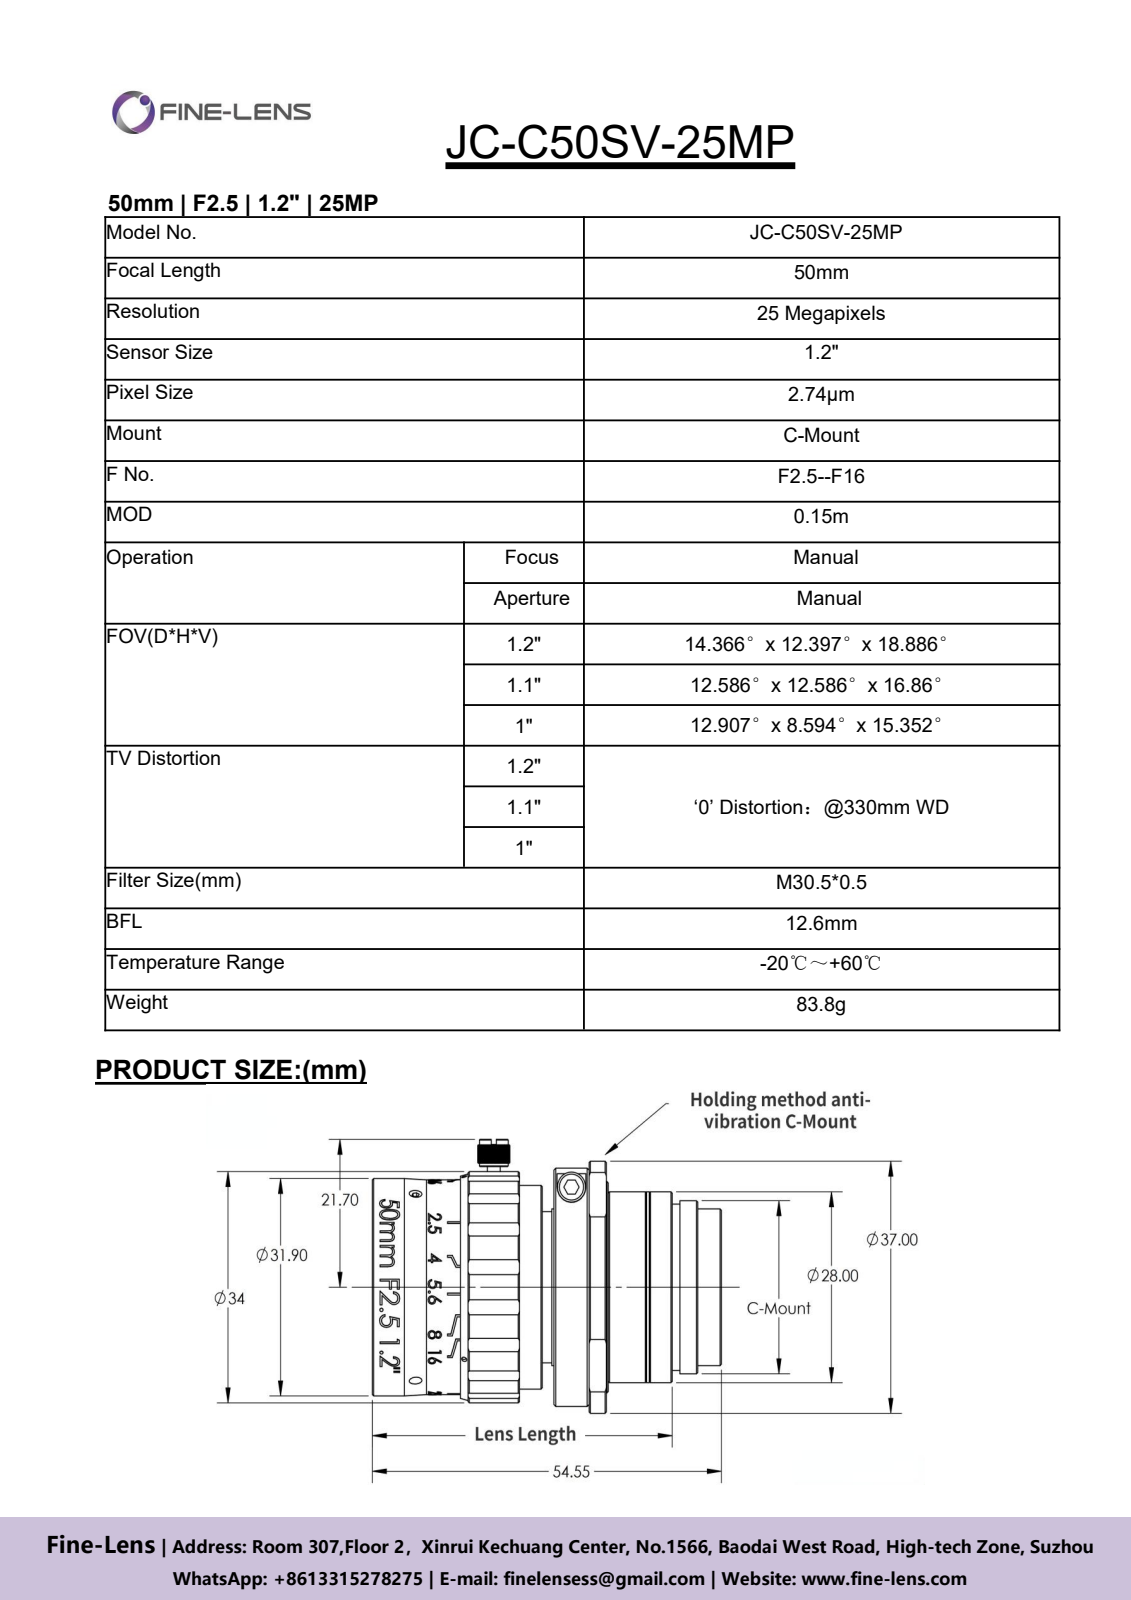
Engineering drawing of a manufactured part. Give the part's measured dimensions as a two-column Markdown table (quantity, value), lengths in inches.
| quantity | value |
| --- | --- |
| part name | 10mmC接口延长圈 |
| STEP written by | SolidWorks 2018 (CONFIG_CONTROL_DESIGN) |
| units | inches |
| bodies | 6 solids, 984 faces (322 planar, 229 cylindrical, 433 other) |
| overall size | 2.148 × 1.457 × 1.457 |
| volume | 2.267 in³ |
| surface area | 29.93 in² |
| round holes (diameter × count) | 0.031 × 3, 0.079 × 3, 0.063 × 1, 0.876 × 1, 0.909 × 1, 0.913 × 1, 0.945 × 1, 0.969 × 1, 1.008 × 1, 1.039 × 1, 1.063 × 1, 1.181 × 1 |
| round bosses / shafts (diameter × count) | 1.378 × 1, 1.256 × 1, 1.244 × 1, 1.24 × 1, 1.22 × 1, 1.177 × 1, 1.102 × 1, 1.031 × 1 |
| partial cylindrical surfaces (radius × count) | 0.098 × 22, 0.02 × 2, 0.63 × 1, 0.669 × 1, 0.728 × 1 |
| main face-to-face distances | 1.146, 0.93, 0.217, 0.335, 1.961, 1.031, 0.814, 1.265, 0.118, 0.696 |
